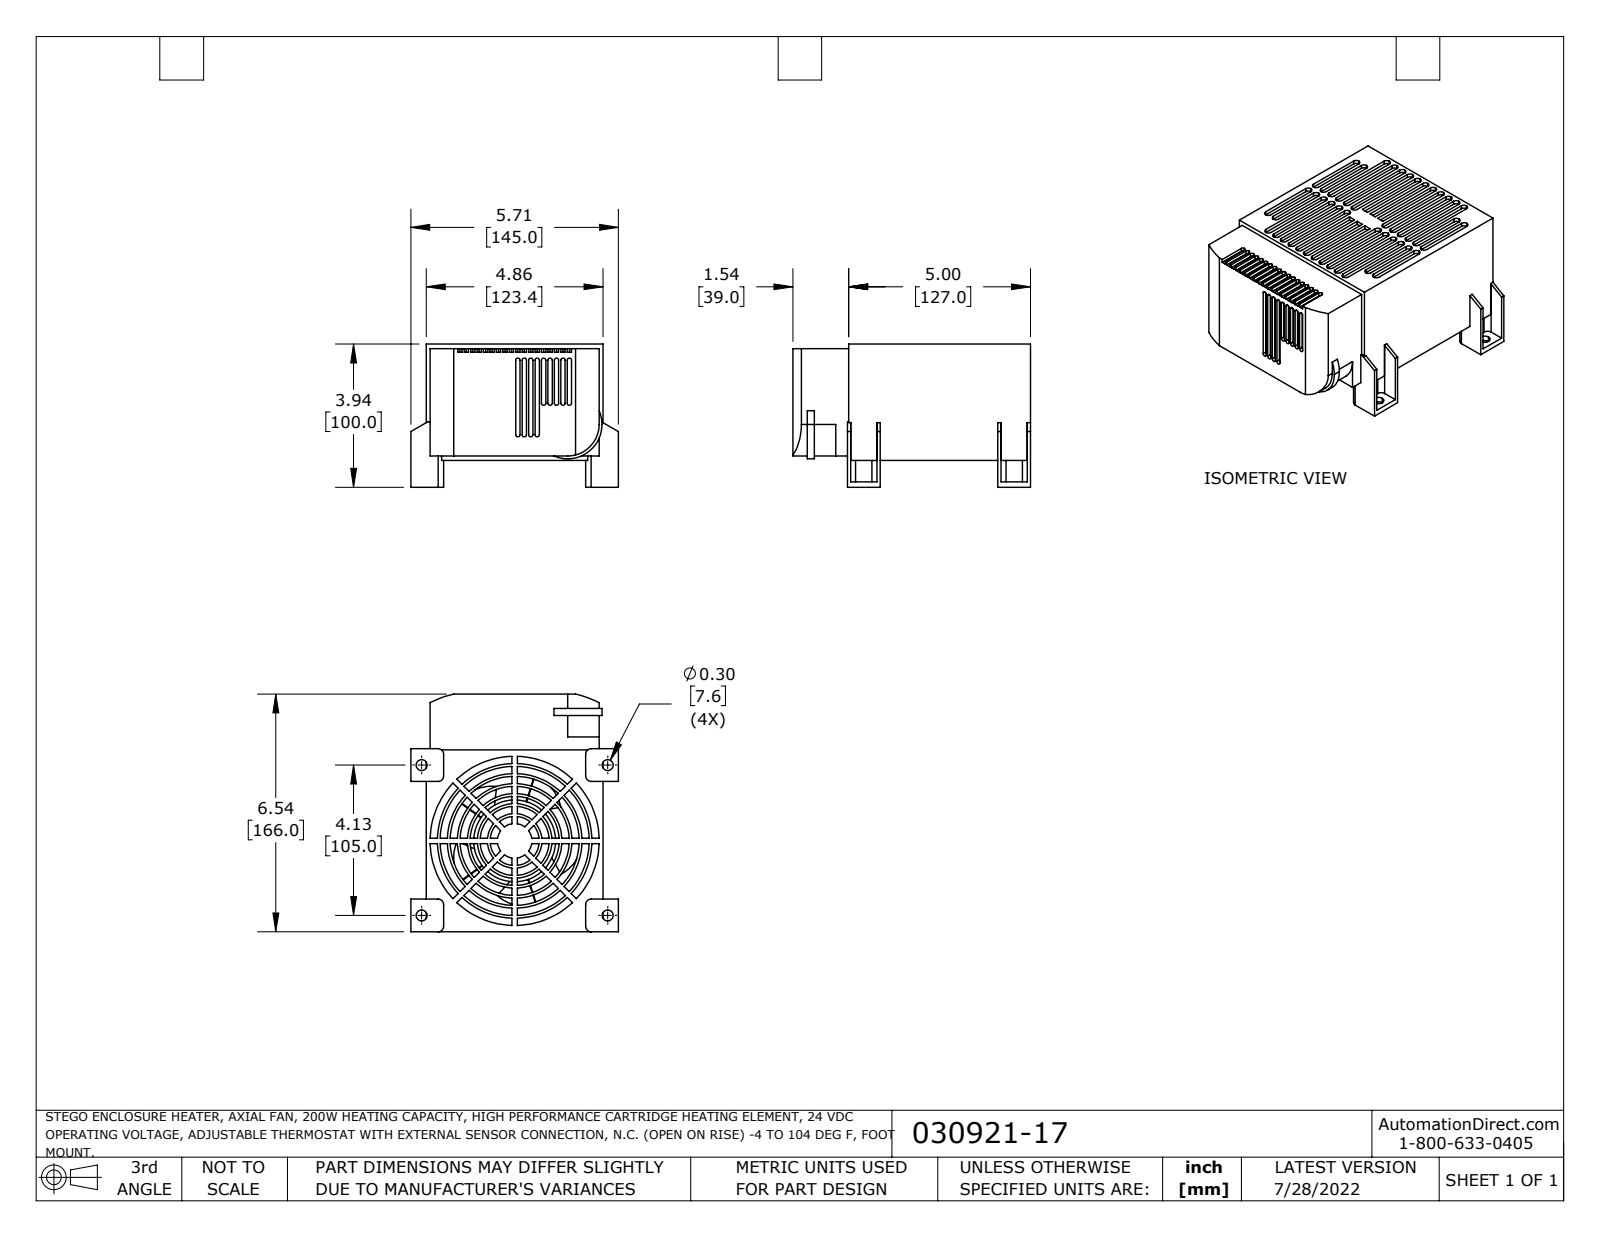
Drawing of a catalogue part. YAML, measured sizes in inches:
part_name: "030921-17_Default"
step_written_by: "SolidWorks 2021 (CONFIG_CONTROL_DESIGN)"
units: inches
bodies: {solids: 1, faces: 703, planar: 474, cylindrical: 229, other: 0}
overall_size: [6.535, 5.709, 3.937]
volume: 84.39
surface_area: 240.1
round_holes:
  - {diameter: 0.3, count: 4}
  - {diameter: 0.394, count: 1}
  - {diameter: 1.35, count: 1}
  - {diameter: 1.9, count: 1}
  - {diameter: 2.45, count: 1}
  - {diameter: 3, count: 1}
  - {diameter: 3.55, count: 1}
  - {diameter: 4.1, count: 1}
  - {diameter: 4.65, count: 1}
round_bosses_or_shafts:
  - {diameter: 4.25, count: 1}
  - {diameter: 3.7, count: 1}
  - {diameter: 3.15, count: 1}
  - {diameter: 2.6, count: 1}
  - {diameter: 2.25, count: 1}
  - {diameter: 2.05, count: 1}
  - {diameter: 1.5, count: 1}
  - {diameter: 0.95, count: 1}
partial_cylinders:
  - {radius: 0.1, count: 54}
  - {radius: 0.059, count: 36}
  - {radius: 0.135, count: 8}
  - {radius: 0.15, count: 8}
  - {radius: 1.086, count: 5}
  - {radius: 2.756, count: 2}
  - {radius: 0.866, count: 1}
  - {radius: 0.945, count: 1}
face_to_face_distances: [0.1, 4.86, 2.1, 0.124, 1, 3.1, 3.2, 2.2, 3.076, 0.4]
hole_center_spacings: [3.279, 3.3, 4.134, 5.118, 6.579]
